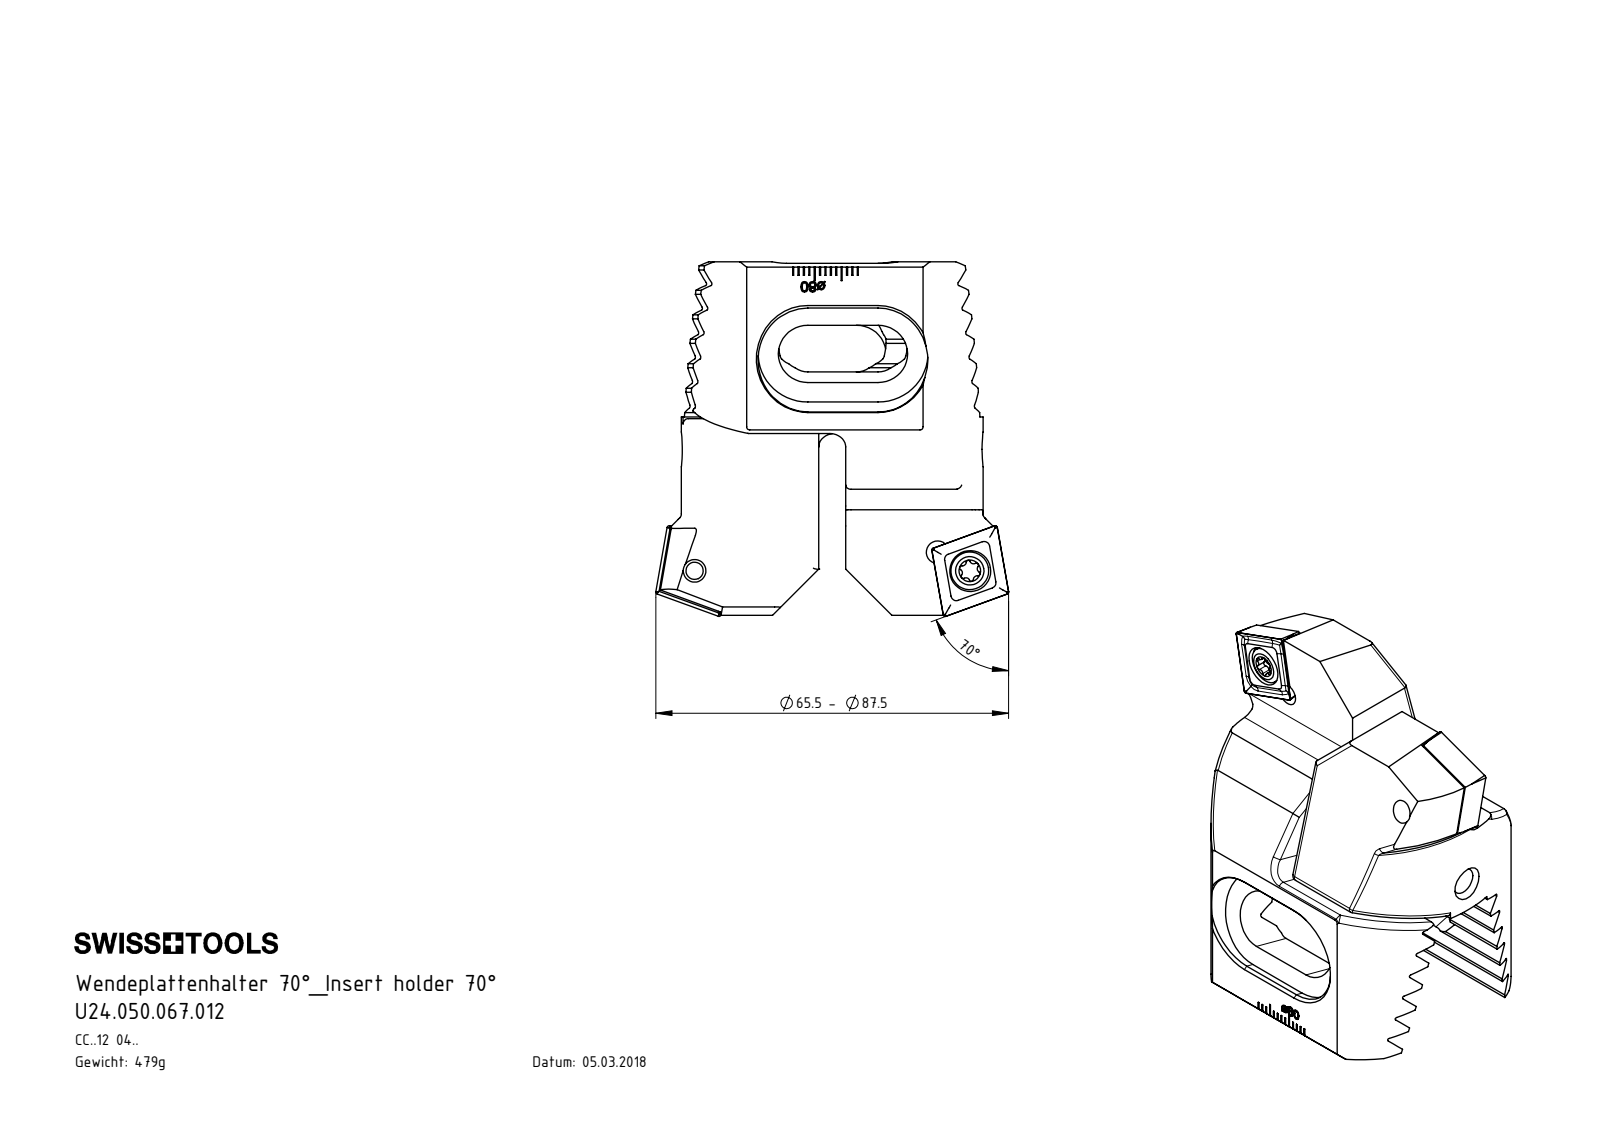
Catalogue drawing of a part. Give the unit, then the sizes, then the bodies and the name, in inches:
Units: inches
Overall size (bounding box): 2.591 × 2.579 × 1.74
Round holes (diameter × count): ⌀0.165 ×4, ⌀0.079 ×2, ⌀0.217 ×2, ⌀0.299 ×2, ⌀0.197 ×1
Round bosses / shafts (diameter × count): ⌀0.276 ×2, ⌀0.197 ×2, ⌀0.236 ×1, ⌀0.157 ×1
Partial cylindrical surfaces — rounded edges, fillets, slot ends (radius × count): R0.039 ×14, R0.013 ×12, R0.015 ×12, R0.027 ×6, R0.027 ×6, R0.118 ×6, R0.217 ×4, R0.364 ×4
Main face-to-face distances: 0.16, 0.32, 0.481, 0.641, 0.801, 0.309, 0.067, 0.858, 0.882, 0.197
Hole centre spacings: 0.271, 0.275, 0.63, 1.781, 1.785, 2.014, 1.217, 1.542
Volume: 3.776 in³ · Surface area: 35.27 in²
Bodies: 8 solids, 622 faces (336 planar, 100 cylindrical, 186 other)
Part name (STEP PRODUCT): Z55.WCC.B70.037; Z55-xxx.001.037_C_CC 12 70ø; CCMT120404; Z55-ER3.001.020 (+1 more)
STEP written by: SolidWorks 2017 (AUTOMOTIVE_DESIGN)
